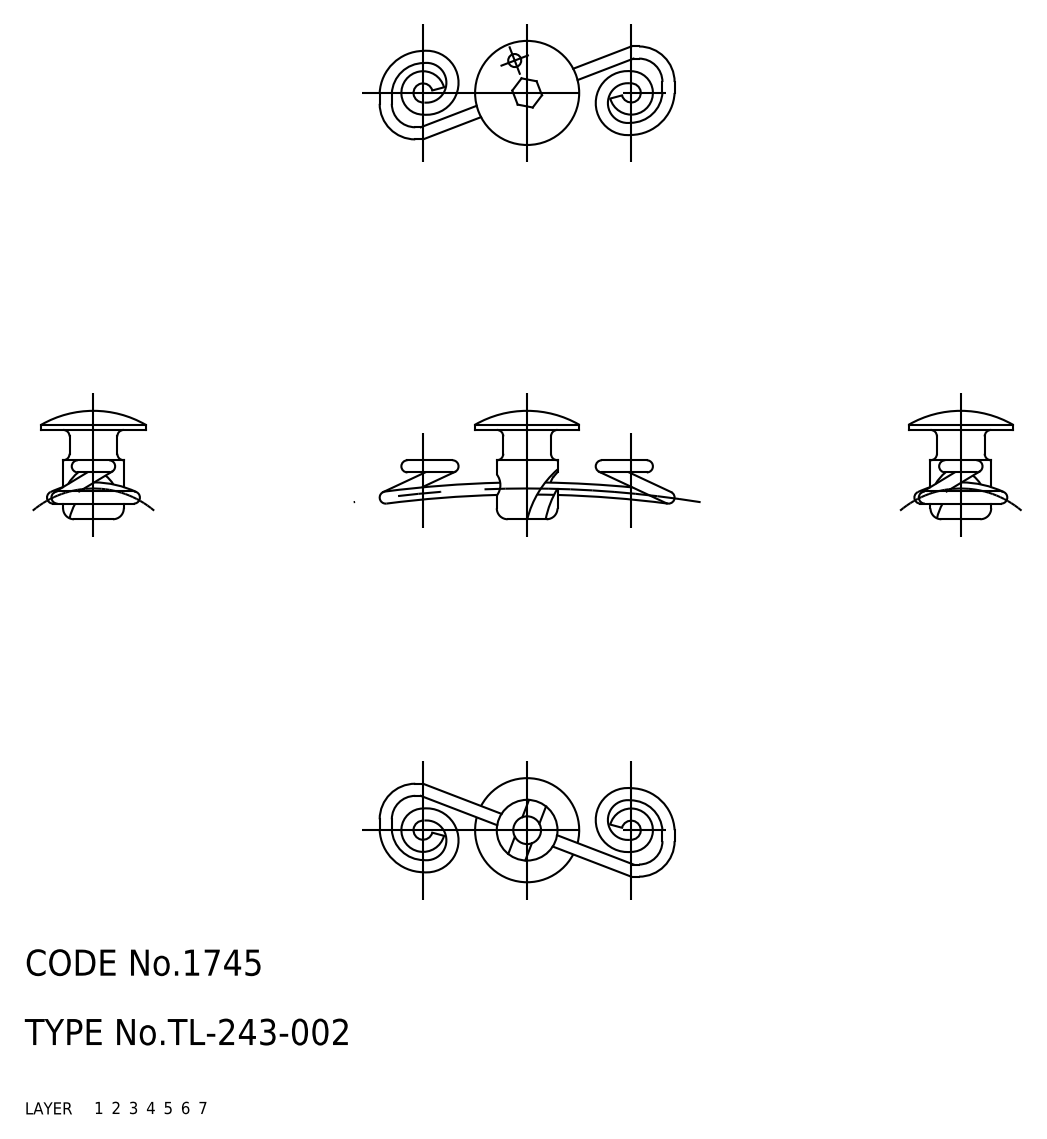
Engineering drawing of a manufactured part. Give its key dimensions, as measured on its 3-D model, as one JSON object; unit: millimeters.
{"part_name": "spring; fastener; TL_243_002_31687_36", "step_written_by": "CADfix (AUTOMOTIVE_DESIGN)", "units": "millimeters", "bodies": {"solids": 2, "faces": 60, "planar": 0, "cylindrical": 0, "other": 60}, "overall_size": [34.02, 12.41, 12], "volume_mm3": 514, "surface_area_mm2": 960}
